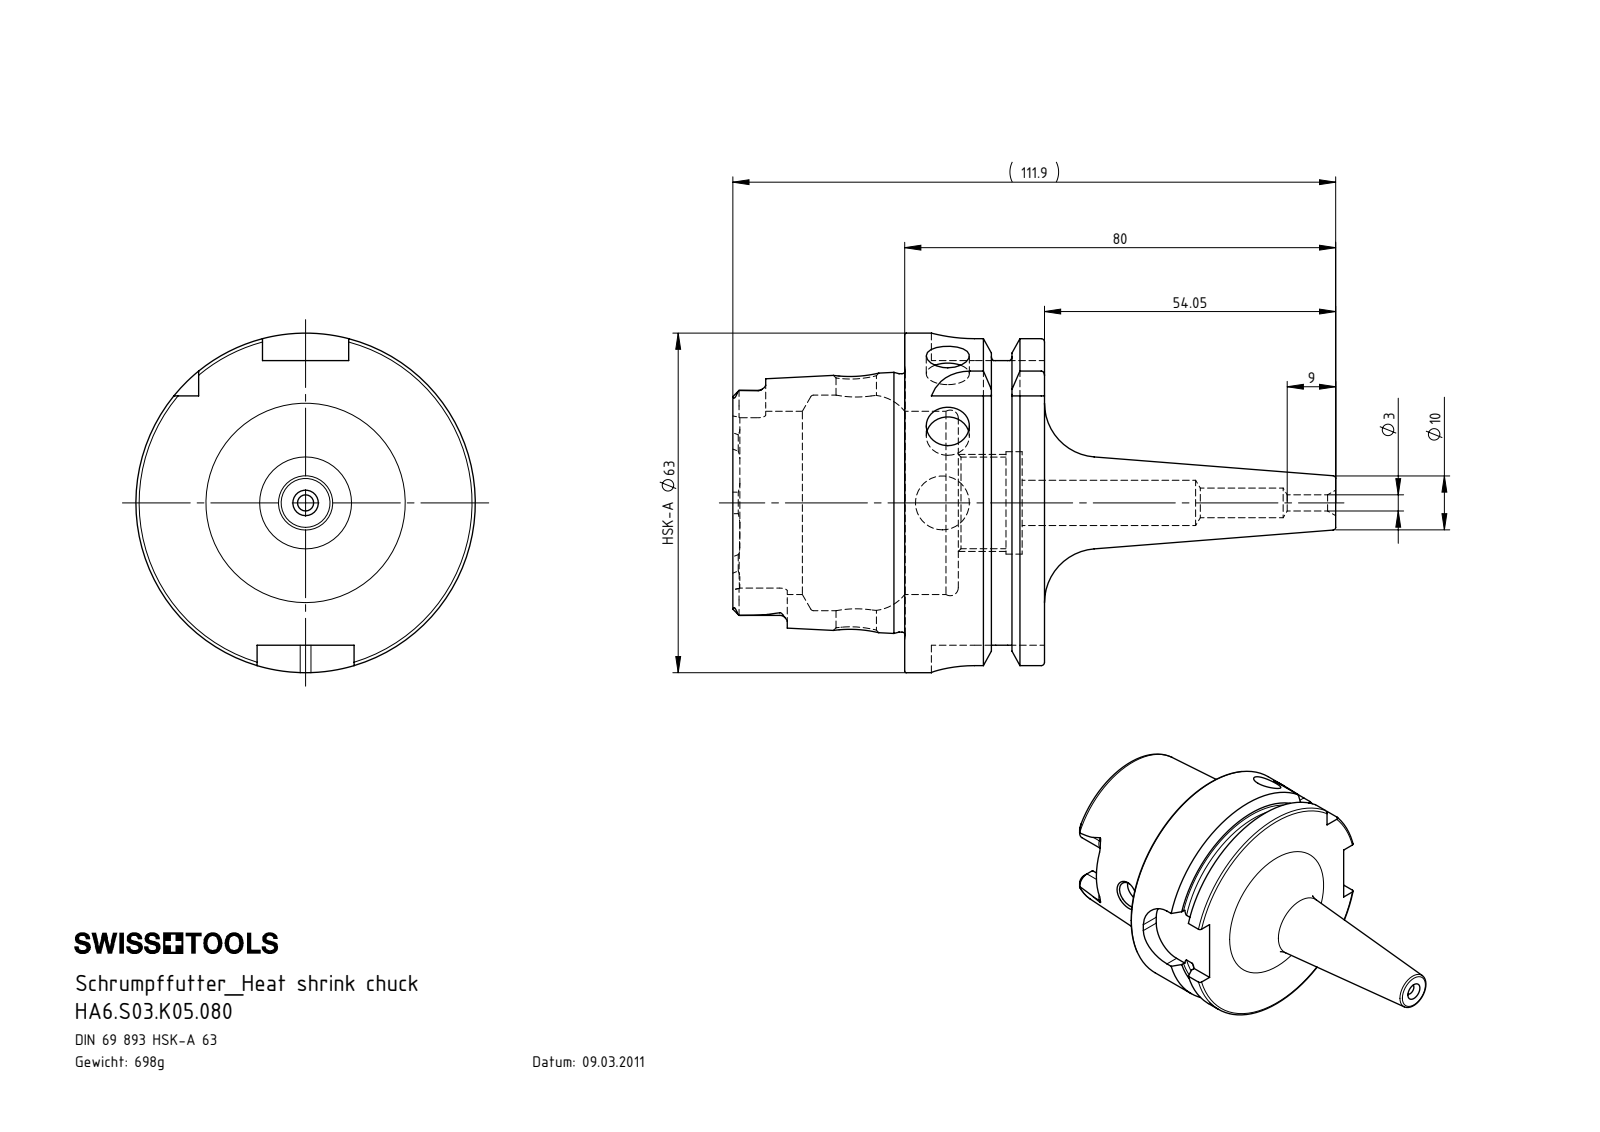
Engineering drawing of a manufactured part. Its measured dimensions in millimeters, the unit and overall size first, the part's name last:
Units: millimetres
Overall size (bounding box): 111.9 × 63 × 63
Round holes (diameter × count): ⌀8 ×2, ⌀3 ×1, ⌀5.5 ×1, ⌀7.5 ×1, ⌀8.4 ×1, ⌀10 ×1, ⌀17 ×1, ⌀19 ×1, ⌀34 ×1, ⌀40 ×1
Round bosses / shafts (diameter × count): ⌀63 ×1, ⌀54.95 ×1, ⌀47.94 ×1
Partial cylindrical surfaces — rounded edges, fillets, slot ends (radius × count): R1.4 ×6, R2.88 ×4, R8 ×4
Main face-to-face distances: 25.95, 16, 9.95, 31.9, 41.85, 57.85, 52.8, 21.8, 11.85, 53.7
Volume: 88 958 mm³ · Surface area: 25 671 mm²
Bodies: 1 solid, 139 faces (48 planar, 34 cylindrical, 57 other)
Part name (STEP PRODUCT): HA6.S03.K05.080
STEP written by: SolidWorks 2017 (AUTOMOTIVE_DESIGN)
